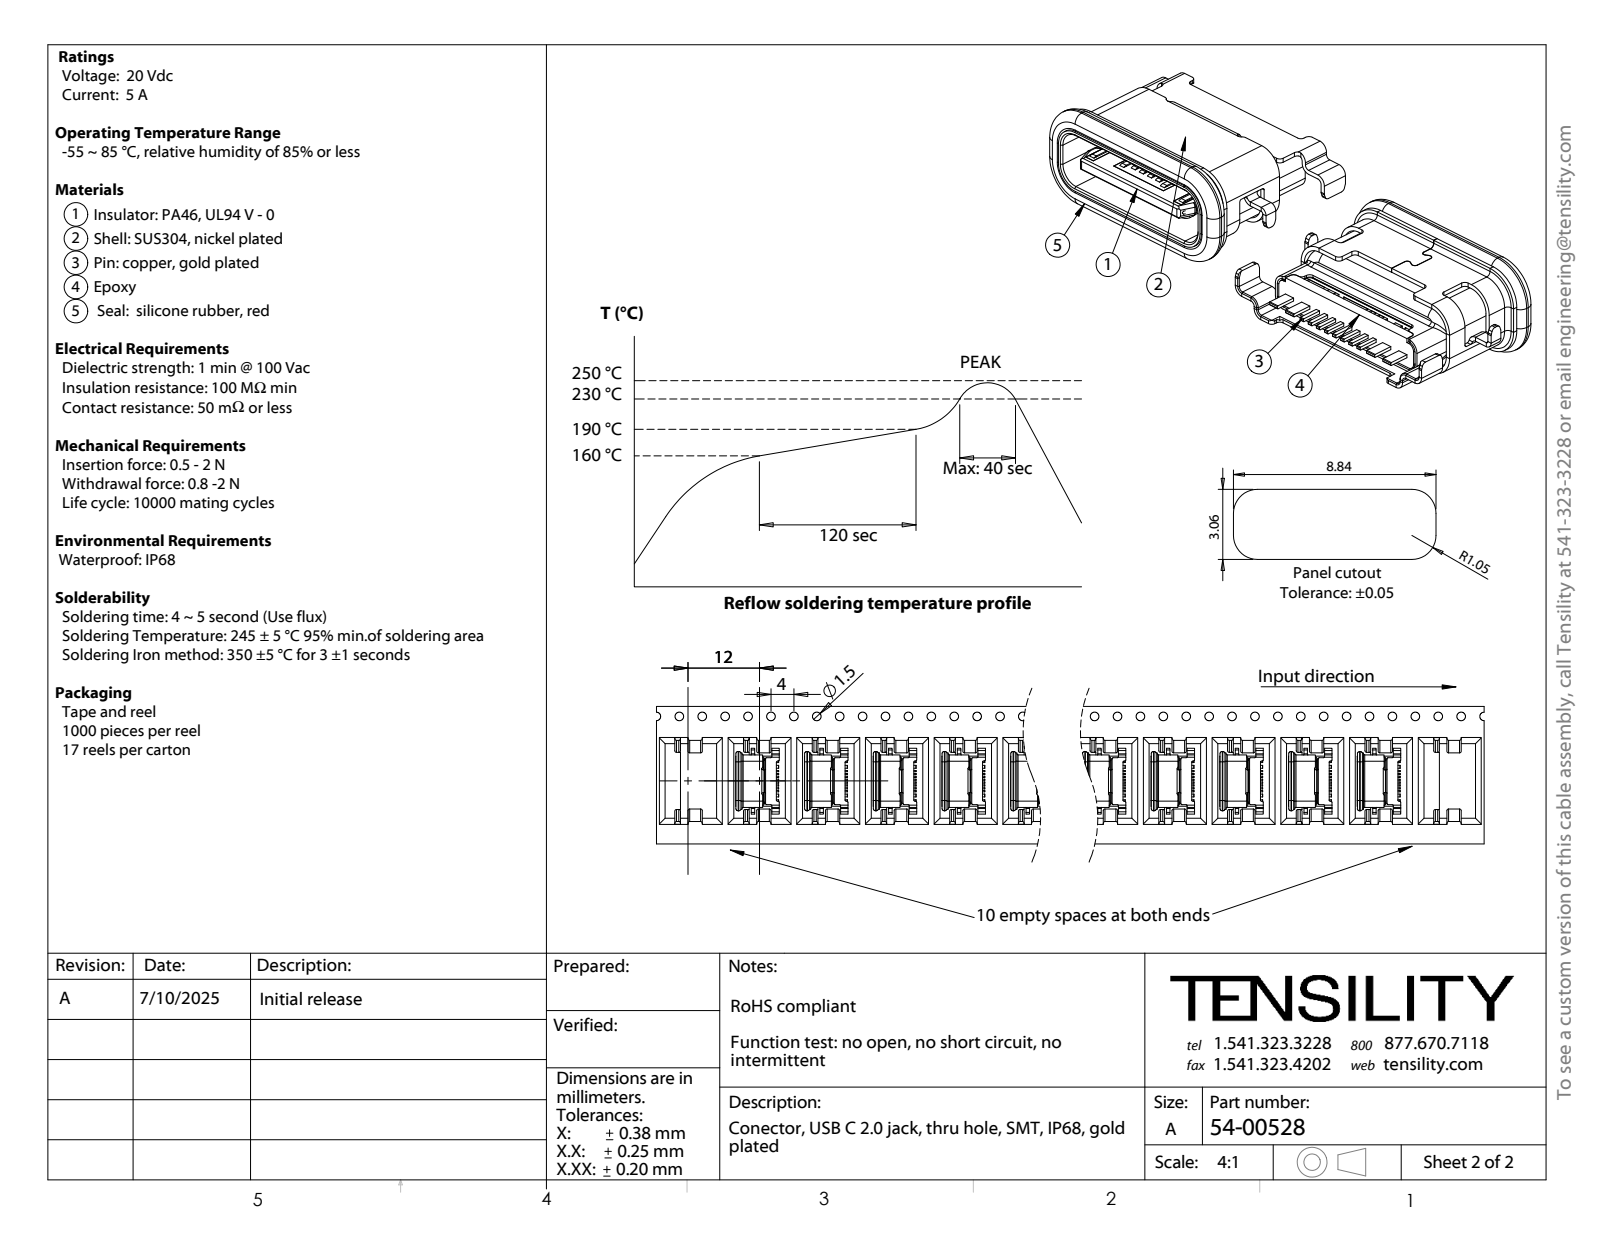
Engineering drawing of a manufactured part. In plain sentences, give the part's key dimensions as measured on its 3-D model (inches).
The part is named "54-00528". Its 3-D file was written by "SolidWorks 2025 (CONFIG_CONTROL_DESIGN)". It is 3 solids with 2367 faces: 1687 planar, 518 cylindrical and 162 other. Overall it measures 0.453 by 0.299 by 0.18 inches. Its volume is 0.006 cubic inches and its surface area 1.36 square inches. Partial cylindrical surfaces (rounded edges, fillets, slot ends): 108 of radius 0.008, 66 of radius 0.006, 40 of radius 0.004, 22 of radius 0.016, 14 of radius 0.012, 12 of radius 0.01, 9 of radius 0.018, 6 of radius 0.024. The main face-to-face distances are 0.117, 0.039, 0.07, 0.078, 0.047, 0.109, 0.016, 0.125, 0.026, 0.109.
